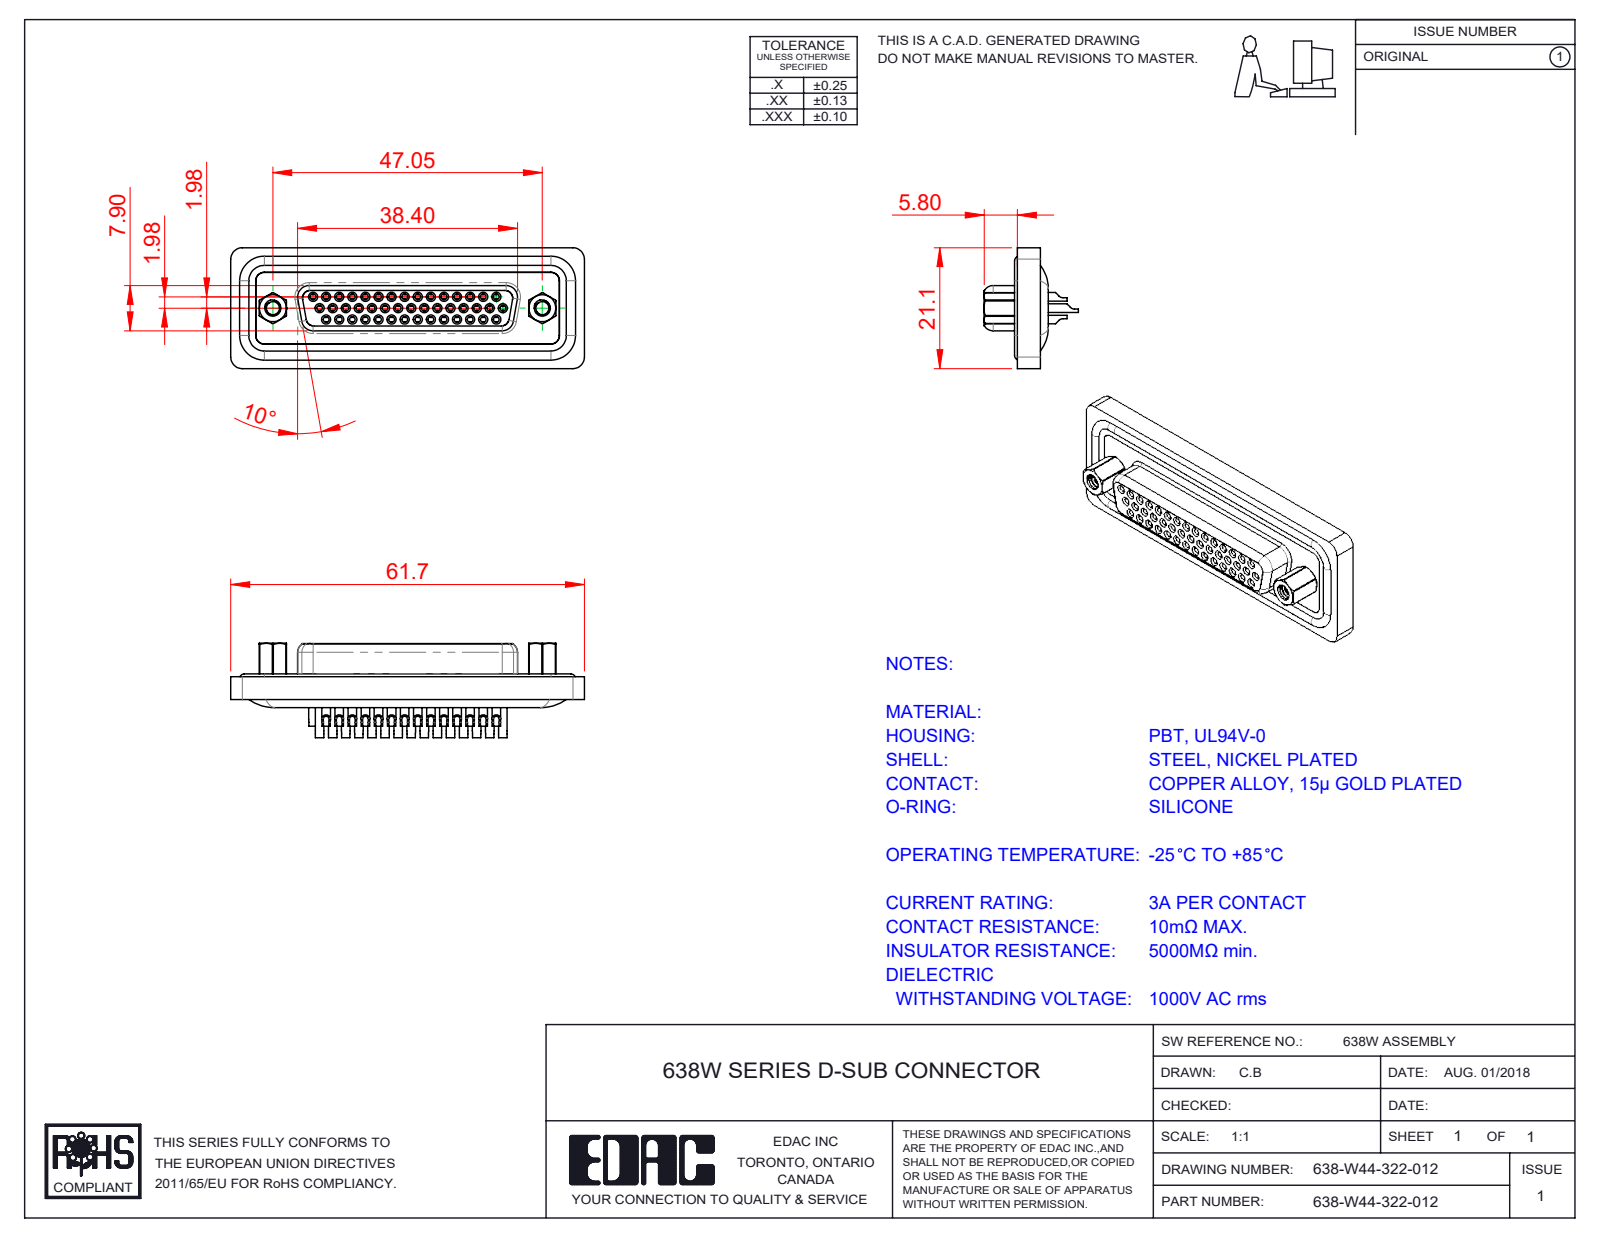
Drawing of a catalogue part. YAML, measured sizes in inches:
part_name: "638W 4-40 Hex Standoff; 638W Contact Row 3_22; 638W Contact Row 2_22; 638W 4-40 Threaded Rivet (+5 more)"
step_written_by: "SolidWorks 2016 (CONFIG_CONTROL_DESIGN)"
units: inches
bodies: {solids: 52, faces: 2929, planar: 849, cylindrical: 1228, other: 852}
overall_size: [2.431, 0.831, 0.65]
volume: 0.441
surface_area: 24.79
round_holes:
  - {diameter: 0.039, count: 44}
  - {diameter: 0.043, count: 44}
  - {diameter: 0.059, count: 44}
  - {diameter: 0.067, count: 44}
  - {diameter: 0.071, count: 44}
  - {diameter: 0.079, count: 44}
  - {diameter: 0.089, count: 2}
  - {diameter: 0.09, count: 2}
  - {diameter: 0.157, count: 2}
  - {diameter: 0.189, count: 2}
  - {diameter: 0.197, count: 2}
round_bosses_or_shafts:
  - {diameter: 0.063, count: 48}
  - {diameter: 0.087, count: 44}
  - {diameter: 0.059, count: 23}
  - {diameter: 0.193, count: 2}
  - {diameter: 0.11, count: 2}
  - {diameter: 0.197, count: 1}
partial_cylinders:
  - {radius: 0.079, count: 14}
  - {radius: 0.059, count: 13}
  - {radius: 0.053, count: 9}
  - {radius: 0.106, count: 6}
  - {radius: 0.02, count: 4}
  - {radius: 0.035, count: 4}
  - {radius: 0.063, count: 4}
  - {radius: 0.069, count: 4}
face_to_face_distances: [0.016, 0.071, 0.114, 0.063, 0.098, 0.043, 0.293, 0.537, 0.608, 0.222]
hole_center_spacings: [0.09, 0.09, 0.156, 0.18, 0.324, 0.27, 0.45, 0.59]
